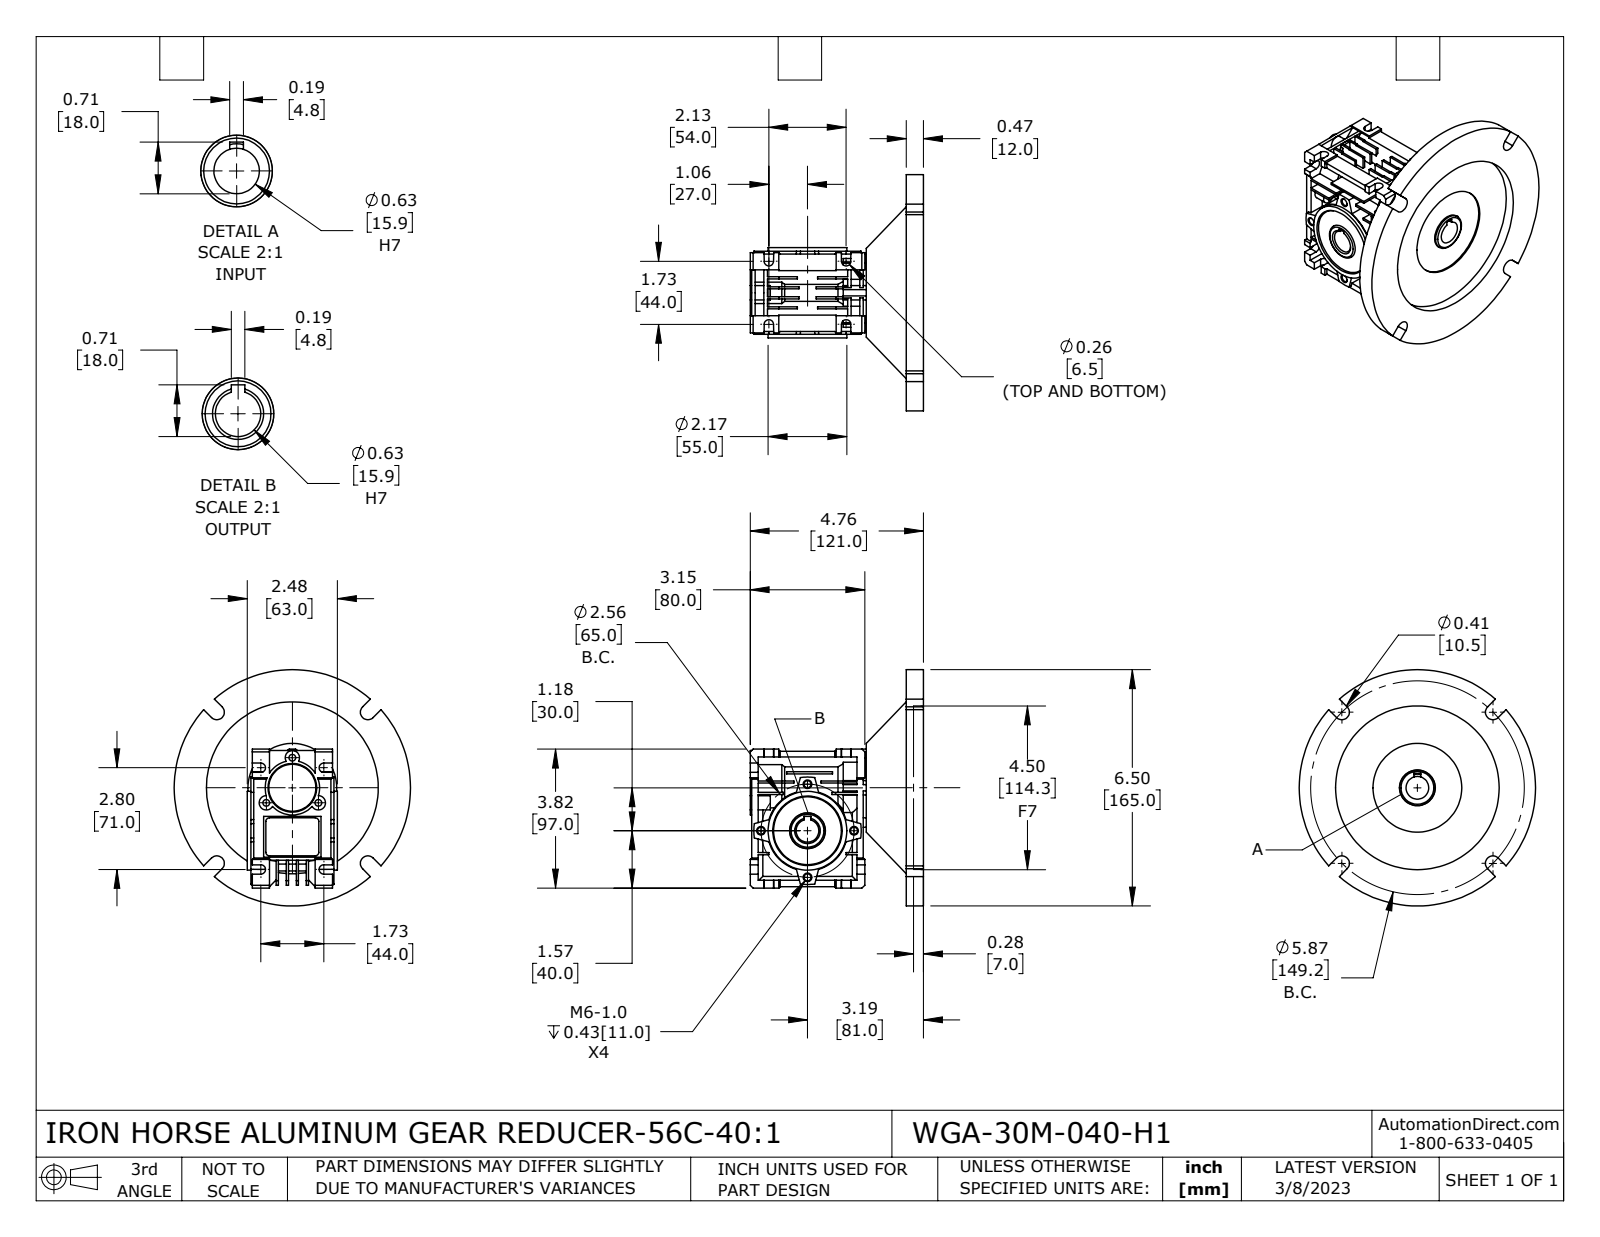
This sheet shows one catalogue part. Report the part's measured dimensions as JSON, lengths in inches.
{"part_name": "WGA-30M-040-H1", "step_written_by": "SolidWorks 2021 (CONFIG_CONTROL_DESIGN)", "units": "inches", "bodies": {"solids": 1, "faces": 682, "planar": 442, "cylindrical": 168, "other": 72}, "overall_size": [6.496, 6.496, 4.764], "volume_in3": 39.8, "surface_area_in2": 198.1, "round_holes": [[0.194, 4], [0.194, 4], [0.183, 3], [0.625, 2], [2.441, 1], [4.5, 1]], "round_bosses_or_shafts": [[6.496, 1], [2.205, 1], [2.165, 1], [1.496, 1], [0.984, 1]], "partial_cylinders_radius": [[0.128, 8], [0.197, 7], [0.098, 4], [0.207, 4], [0.374, 1], [0.669, 1], [0.846, 1], [1.476, 1]], "face_to_face_distances": [0.276, 0.059, 0.039, 0.472, 0.217, 0.197, 0.177, 0.551, 0.335, 0.157], "hole_center_spacings": [1.28, 1.809, 0.827, 1.432, 2.559, 1.432]}
